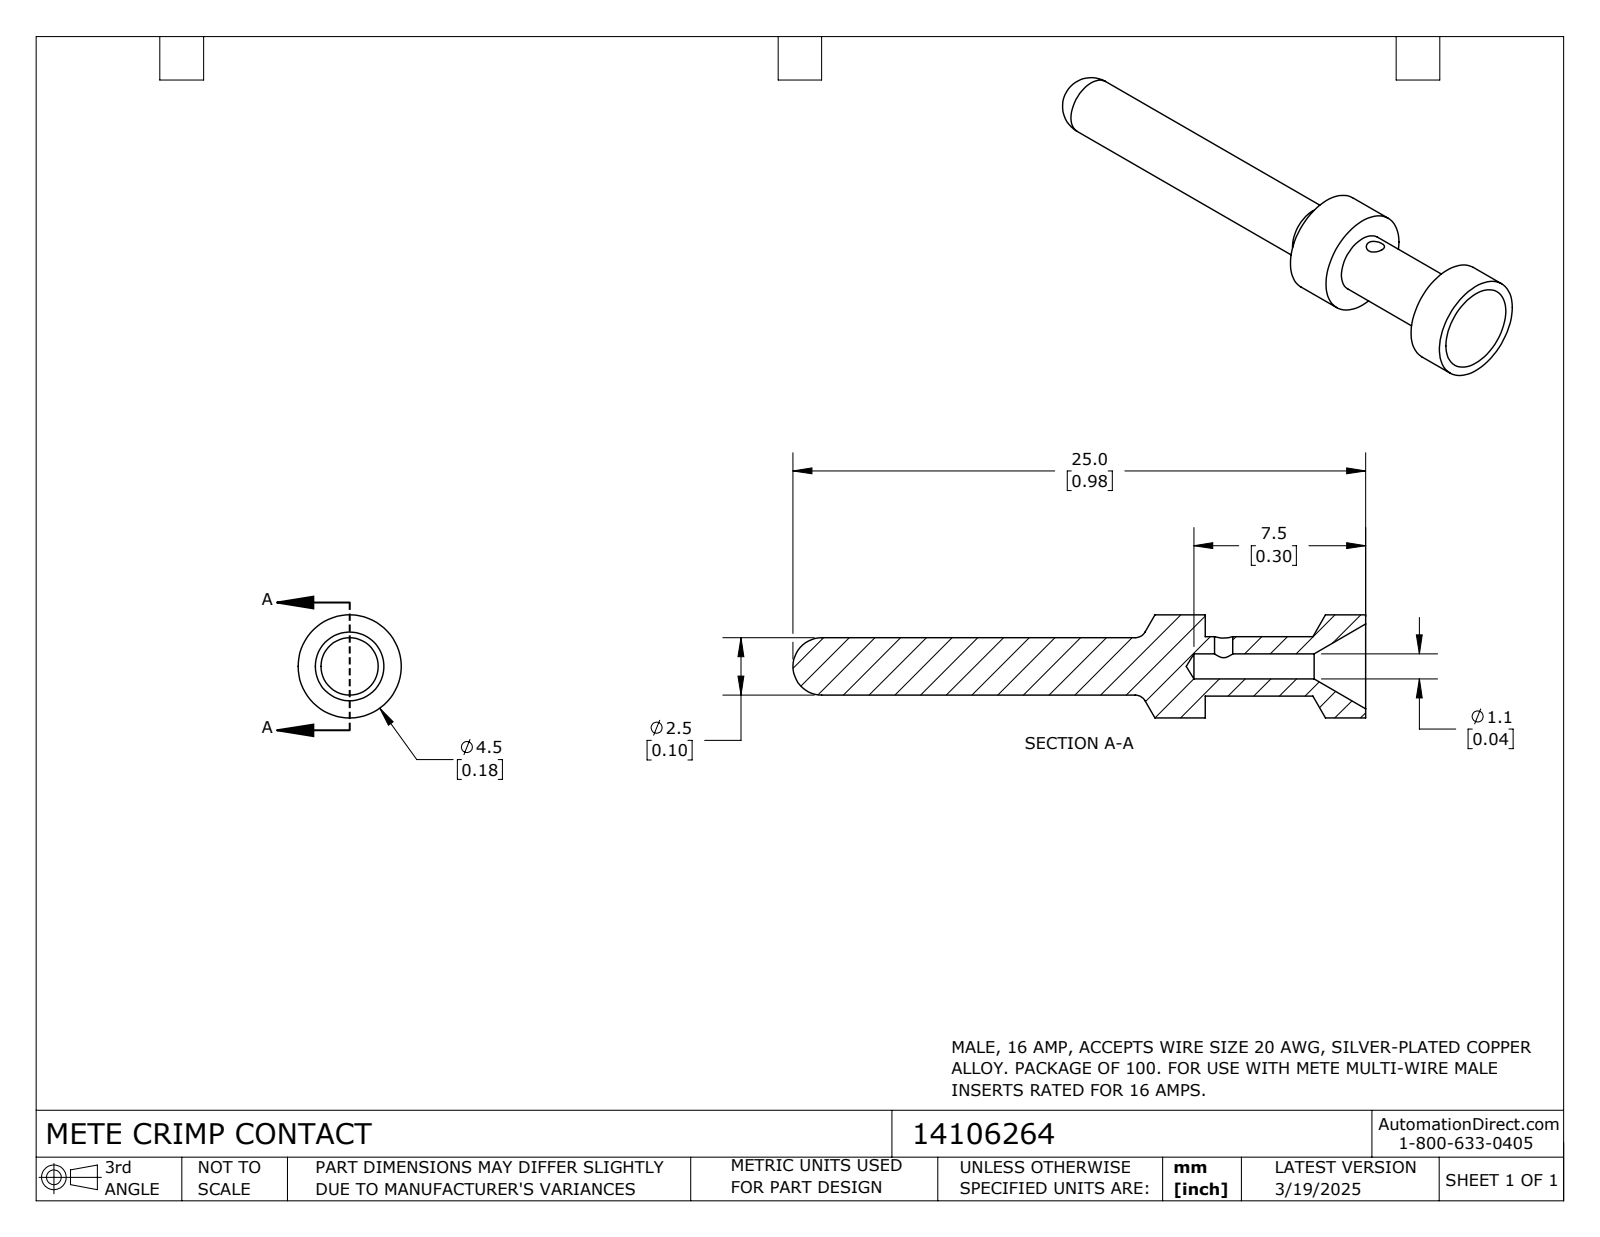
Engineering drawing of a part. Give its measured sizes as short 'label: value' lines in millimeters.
name: 14106264
written by: SolidWorks 2024 (CONFIG_CONTROL_DESIGN)
unit: mm
bodies: 1 solid, 26 faces (2 planar, 12 cylindrical, 12 other)
size: 25 × 4.5 × 4.5
volume: 155 mm³; area: 294 mm²
holes: 1× ⌀0.8, 1× ⌀1.1
bosses: 1× ⌀4.5, 1× ⌀2.6, 1× ⌀2.5
face distances: 7
